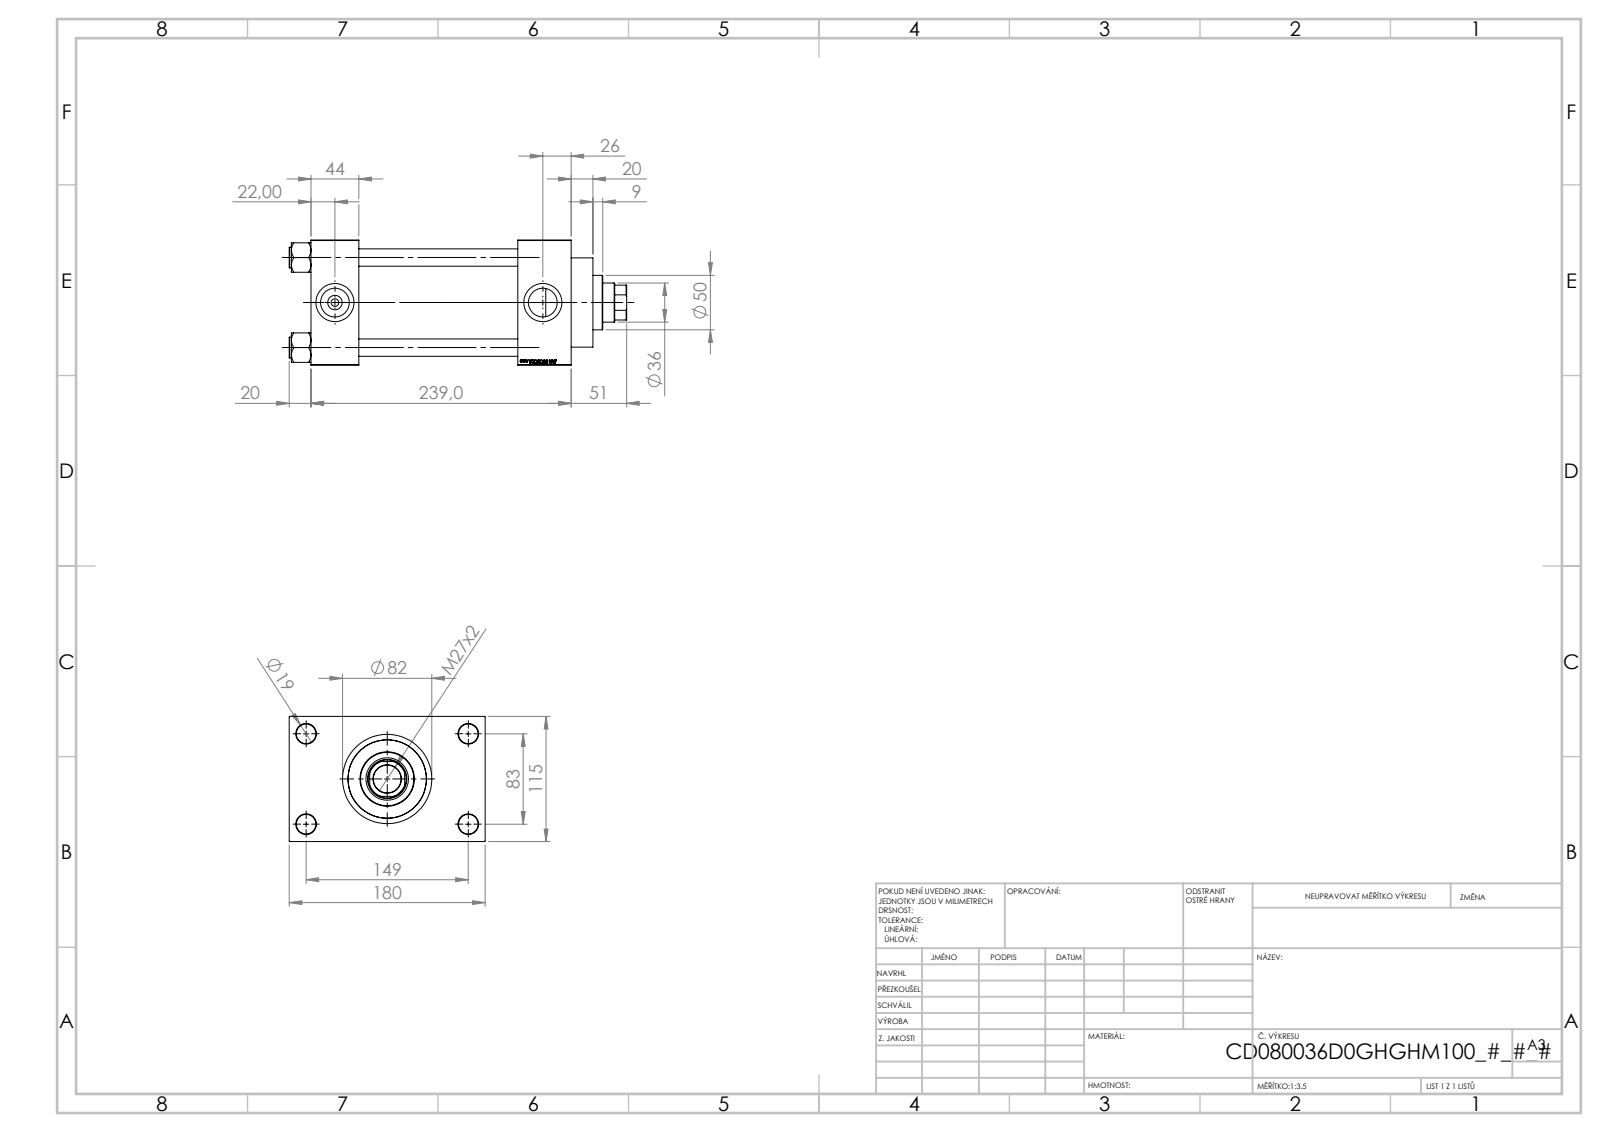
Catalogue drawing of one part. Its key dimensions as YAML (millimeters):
part_name: "V215CD_VCP_D; V215CD_D_Body; V215CD_VC_A; V215CD_D_TYCINKA (+1 more)"
step_written_by: "SolidWorks 2019 (CONFIG_CONTROL_DESIGN)"
units: millimeters
bodies: {solids: 11, faces: 1151, planar: 545, cylindrical: 88, other: 518}
overall_size: [310, 180, 115]
volume: 2188000
surface_area: 363447
round_holes:
  - {diameter: 16, count: 4}
  - {diameter: 18, count: 4}
  - {diameter: 7, count: 2}
  - {diameter: 26.44, count: 2}
  - {diameter: 35, count: 2}
  - {diameter: 25.5, count: 1}
  - {diameter: 36, count: 1}
  - {diameter: 39, count: 1}
  - {diameter: 61, count: 1}
  - {diameter: 72, count: 1}
  - {diameter: 80, count: 1}
round_bosses_or_shafts:
  - {diameter: 19, count: 4}
  - {diameter: 86, count: 1}
  - {diameter: 82, count: 1}
  - {diameter: 50, count: 1}
partial_cylinders:
  - {radius: 17.5, count: 1}
face_to_face_distances: [115, 146, 195, 49, 44, 190, 239, 32.5, 147.5, 180]
hole_center_spacings: [33.15, 58.48, 82.7, 85.28, 89.24, 115.85, 142.43, 83]
